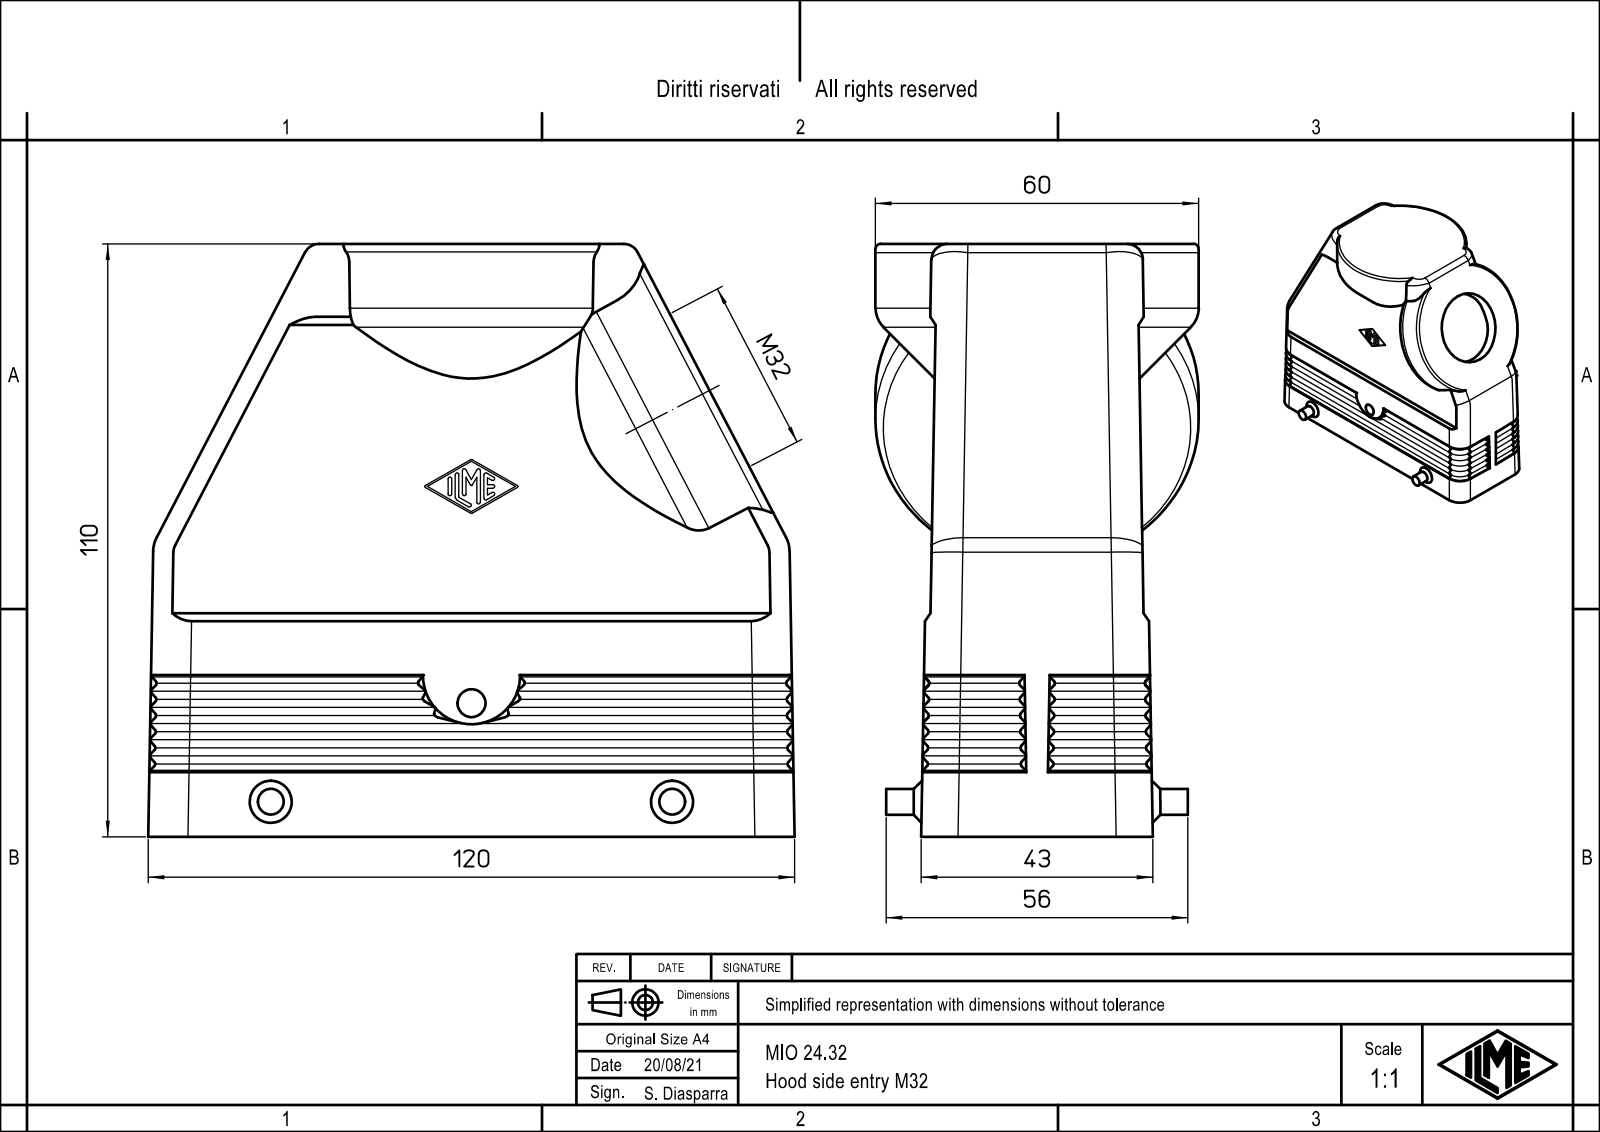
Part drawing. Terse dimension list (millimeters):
name: MIO_24.32
written by: Creo Elements/Direct Modeling 20.1B 02-Apr-2019 (C) Parametric Technology GmbH (AUTOMOTIVE_DESIGN)
unit: mm
bodies: 1 solid, 574 faces (234 planar, 171 cylindrical, 169 other)
size: 119.23 × 109.2 × 60
volume: 116 253 mm³; area: 67 327 mm²
holes: 4× ⌀3.5, 1× ⌀5.2, 1× ⌀32
bosses: 2× ⌀4.8
rounds: 78× R0.5, 10× R3, 8× R7, 4× R4.2, 2× R30, 2× R33.77, 1× R1
face distances: 1.05, 1.06, 2, 5.2, 2.4, 4, 7.95, 5.58, 8.5, 6
hole spacings: 27, 104, 107.45
